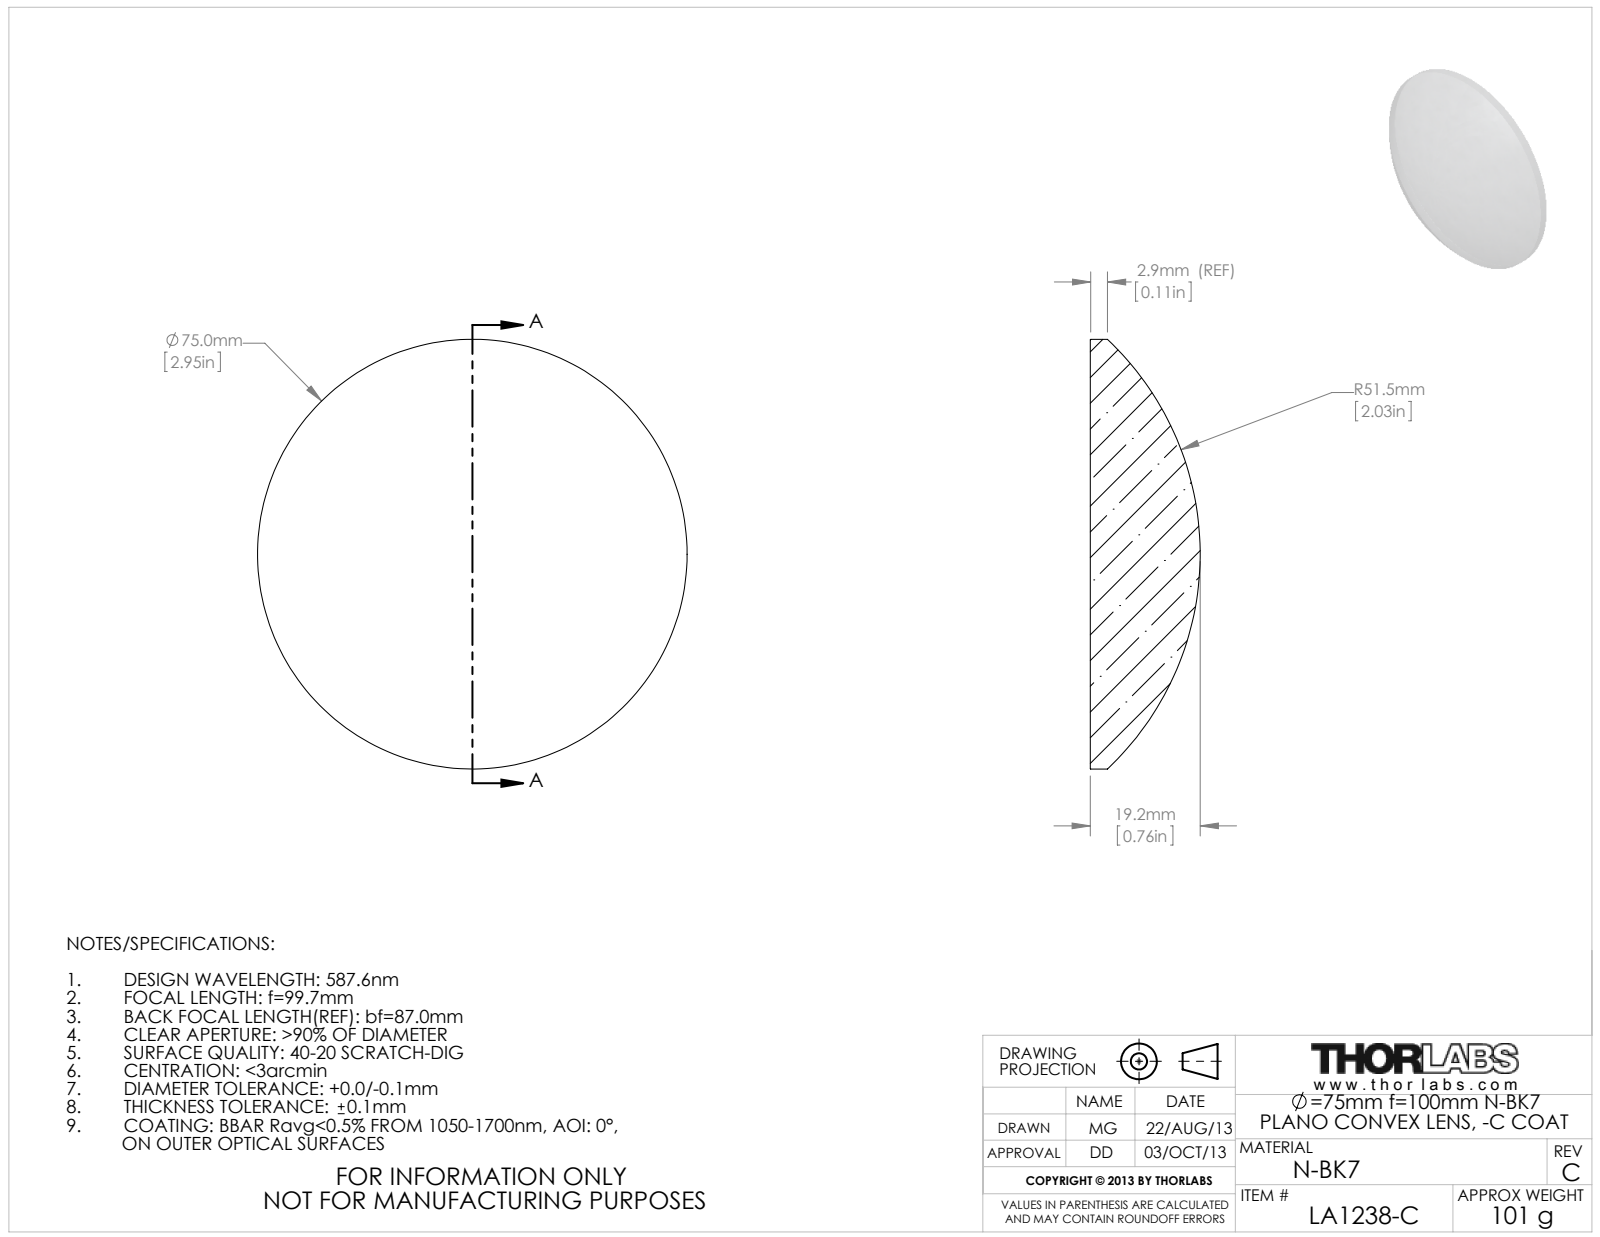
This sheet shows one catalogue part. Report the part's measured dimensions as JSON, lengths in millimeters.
{"part_name": "4614-E0W", "step_written_by": "SolidWorks 2009 (AUTOMOTIVE_DESIGN)", "units": "millimeters", "bodies": {"solids": 0, "faces": 5, "planar": 1, "cylindrical": 2, "other": 2}, "overall_size": [75, 75, 19.19], "round_bosses_or_shafts": [[75, 1]]}
